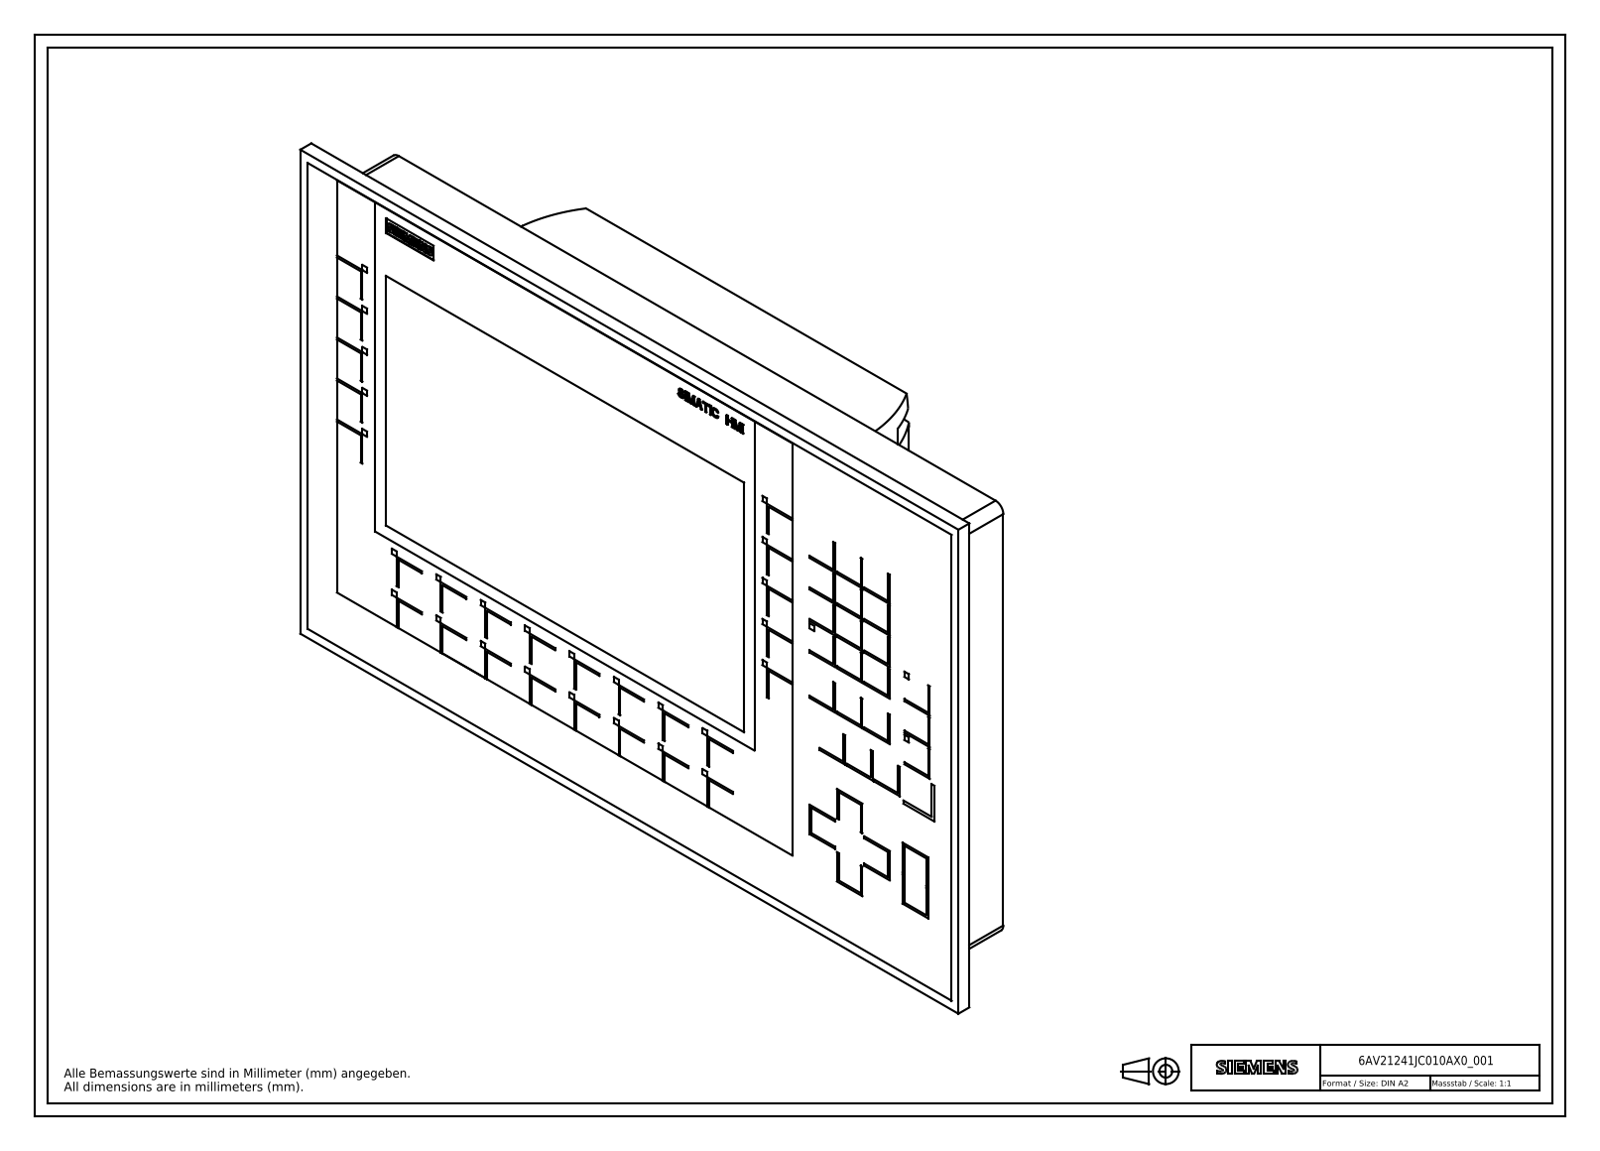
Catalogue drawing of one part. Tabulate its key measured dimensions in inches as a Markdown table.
| quantity | value |
| --- | --- |
| part name | A5E30321192A_001; A5E30293258A_001; A5E30291694A_001; A5E30291692A_001 (+1 more) |
| STEP written by | SIEMENS UGS NX 6.0 (AUTOMOTIVE_DESIGN) |
| units | inches |
| bodies | 347 solids, 3597 faces (2999 planar, 328 cylindrical, 270 other) |
| overall size | 14.22 × 9.055 × 2.72 |
| volume | 176.7 in³ |
| surface area | 629.9 in² |
| round holes (diameter × count) | 0.035 × 9, 0.094 × 2, 0.15 × 2, 0.335 × 2 |
| round bosses / shafts (diameter × count) | 0.217 × 10, 0.276 × 6, 0.118 × 2, 0.038 × 2, 0.031 × 2, 0.315 × 1 |
| partial cylindrical surfaces (radius × count) | 0.008 × 125, 0.004 × 54, 0.012 × 24, 0.031 × 24, 0.033 × 6, 0.118 × 6, 0.018 × 4, 0.073 × 4 |
| main face-to-face distances | 0.224, 1.22, 1.445, 0.194, 1.414, 0.031, 1.443, 0.222, 0.029, 1.26 |
| hole center spacings | 0.121, 0.109, 0.195, 0.217, 0.292, 0.326, 0.276, 0.338 |
